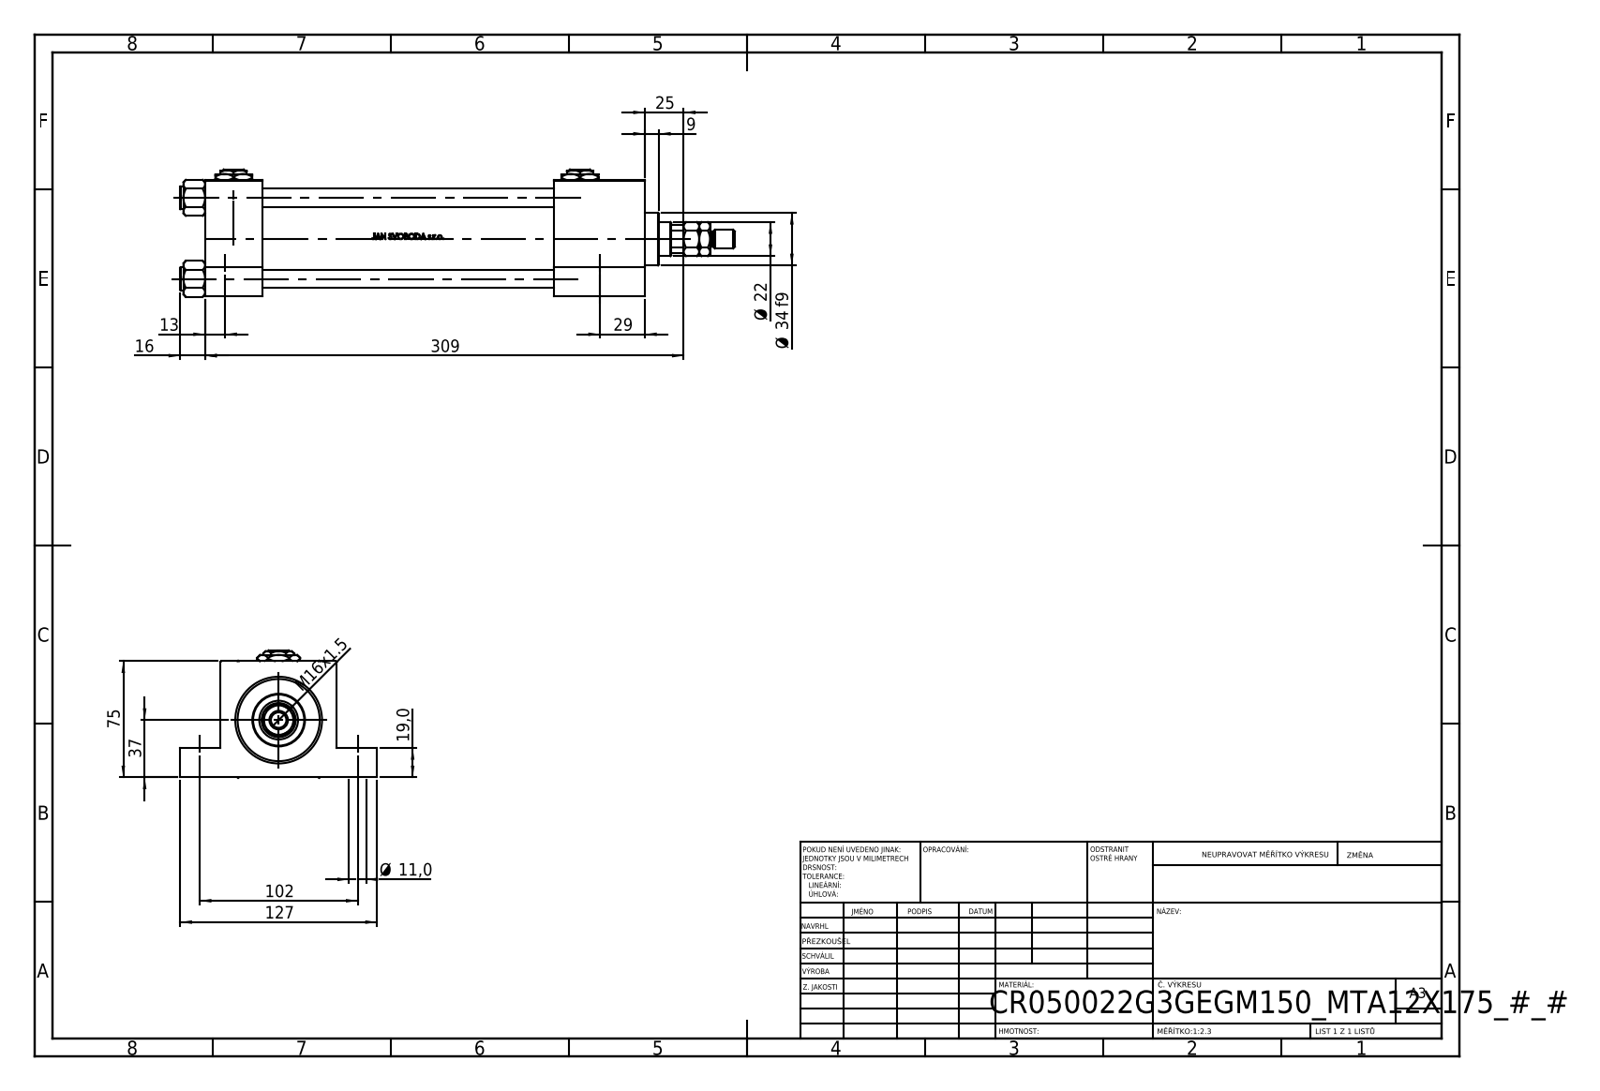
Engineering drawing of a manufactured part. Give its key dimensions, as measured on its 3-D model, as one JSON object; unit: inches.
{"part_name": "V215CR_G_Body; V215CR_VCP_G; MTA; V215_VC_A (+3 more)", "step_written_by": "SolidWorks 2019 (CONFIG_CONTROL_DESIGN)", "units": "inches", "bodies": {"solids": 14, "faces": 1221, "planar": 491, "cylindrical": 128, "other": 602}, "overall_size": [14.094, 5, 3.239], "volume_in3": 57.45, "surface_area_in2": 366.6, "round_holes": [[0.433, 4], [0.472, 4], [0.276, 2], [0.825, 2], [1.181, 2], [0.413, 1], [0.866, 1], [0.984, 1], [1.614, 1], [1.969, 1], [2.087, 1]], "round_bosses_or_shafts": [[0.591, 4], [2.205, 1], [1.339, 1], [0.472, 1], [0.394, 1]], "partial_cylinders_radius": [[0.413, 1]], "face_to_face_distances": [2.953, 1.457, 11.181, 9.724, 0.748, 2.205, 8.858, 7.402, 2.323, 3.976], "hole_center_spacings": [2.059, 1.442, 1.47, 2.02, 2.072, 2.912, 4.016, 9.237]}
